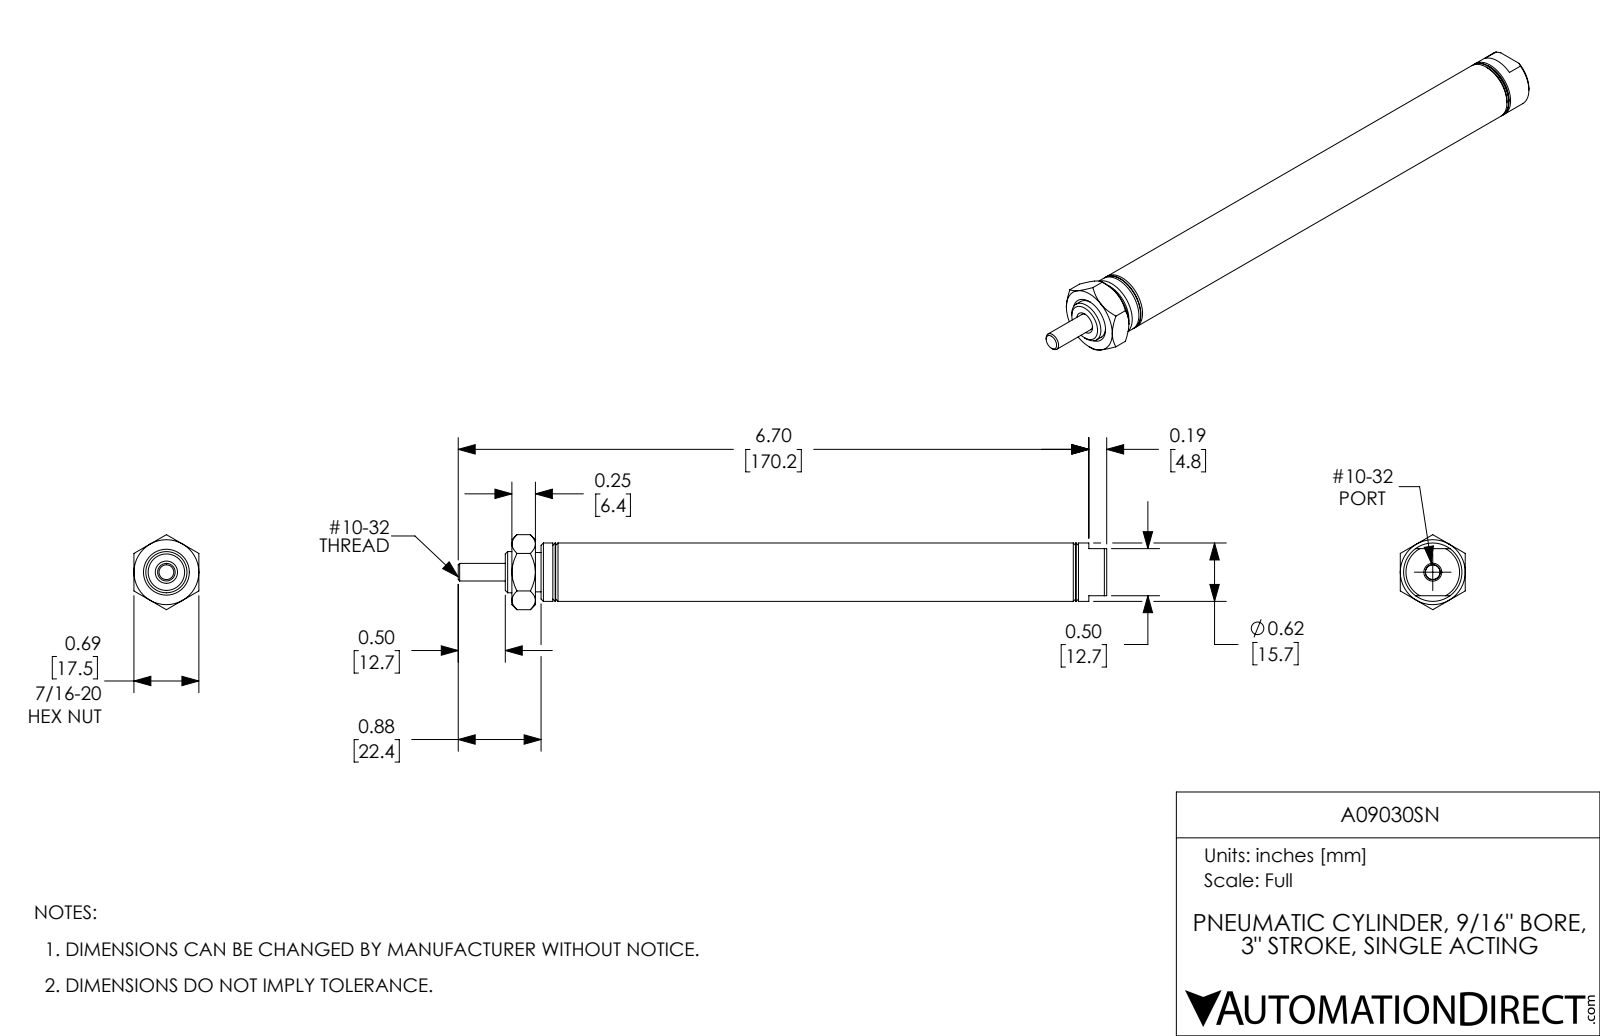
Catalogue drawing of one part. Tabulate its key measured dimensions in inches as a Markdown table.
| quantity | value |
| --- | --- |
| part name | A09030SN-MainBody; A09030SN-Rod; A09030SN_Mounting Nut_D-154; A09030SN |
| STEP written by | SolidWorks 2017 (AUTOMOTIVE_DESIGN) |
| units | inches |
| bodies | 3 solids, 95 faces (27 planar, 30 cylindrical, 38 other) |
| overall size | 6.89 × 0.797 × 0.69 |
| volume | 1.249 in³ |
| surface area | 26.94 in² |
| round holes (diameter × count) | 0.156 × 1, 0.159 × 1, 0.187 × 1, 0.19 × 1, 0.437 × 1, 0.563 × 1 |
| round bosses / shafts (diameter × count) | 0.62 × 1, 0.417 × 1 |
| main face-to-face distances | 1.255, 4.755, 0.5, 0.69, 1.565, 4.565, 3.5, 6.07, 4.815, 1.315 |
